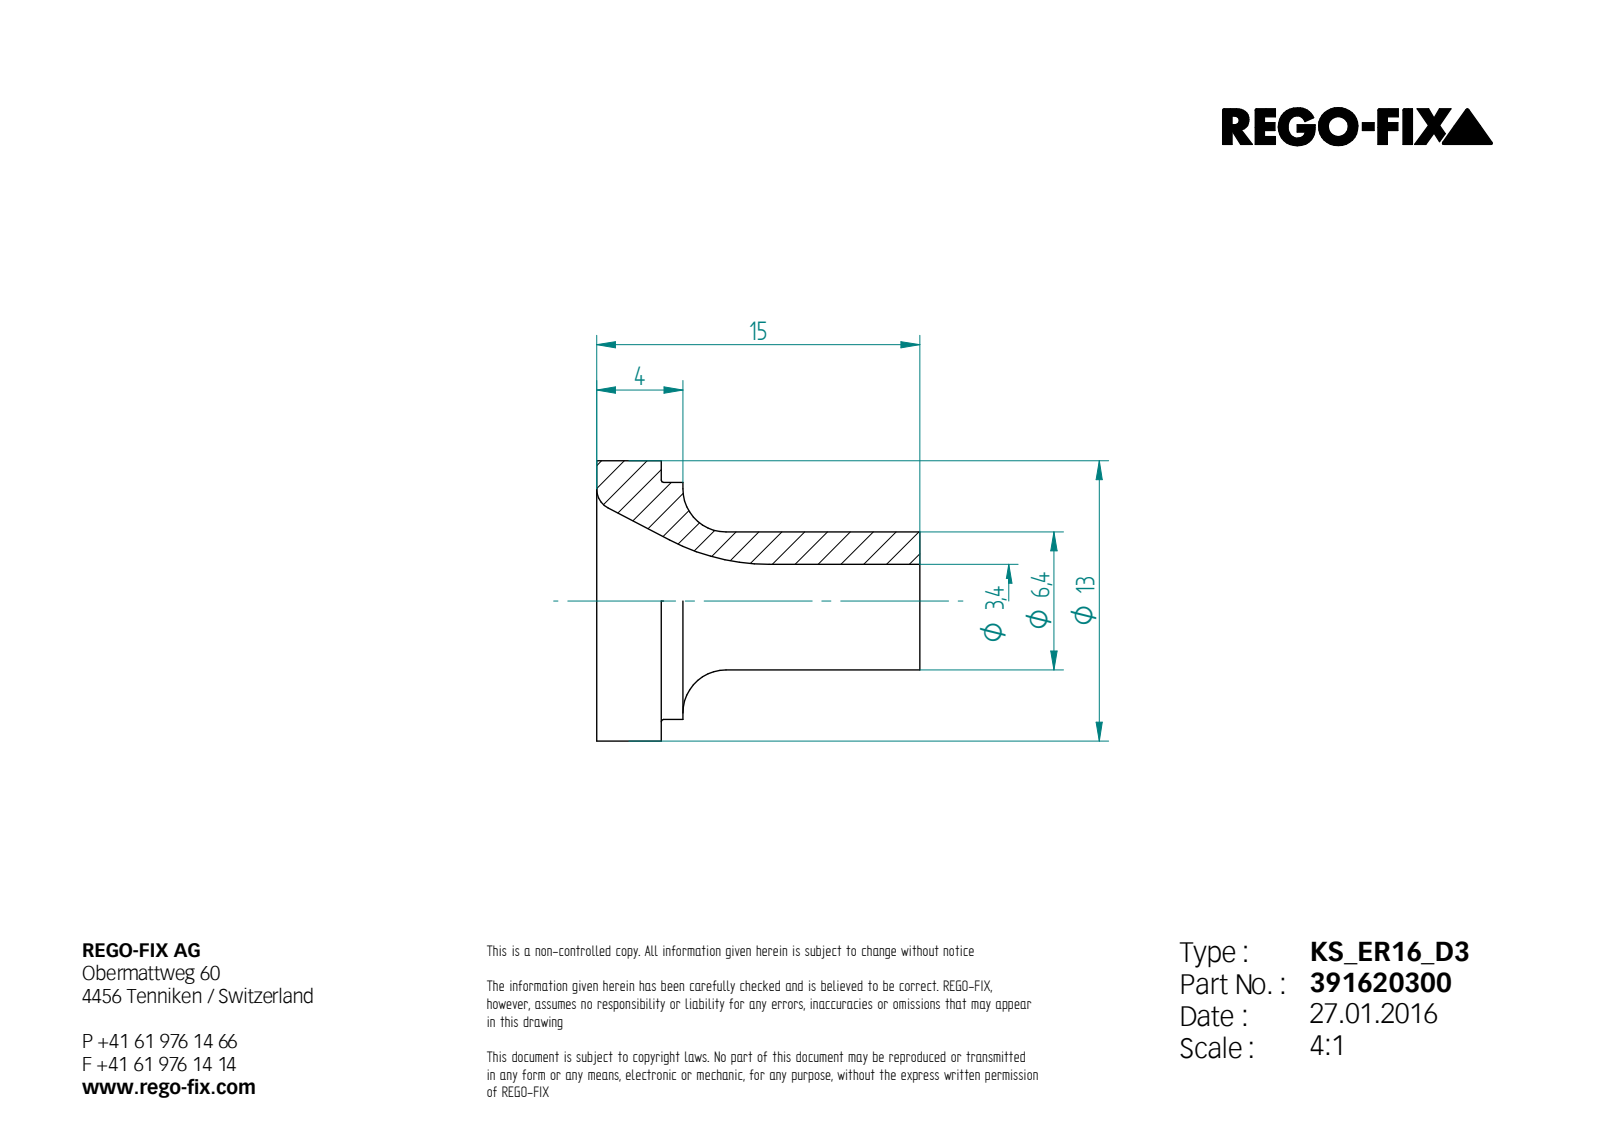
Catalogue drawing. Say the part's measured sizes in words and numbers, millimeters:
Its 3-D file was written by "Unknown (AUTOMOTIVE_DESIGN)". It is 1 solid with 13 faces: 4 planar, 4 cylindrical and 5 other. Overall it measures 15 by 13 by 13 millimeters. Its volume is 589 cubic millimeters and its surface area 774 square millimeters. Round holes: 1 of diameter 3.4. Round bosses or shafts: 1 of diameter 13, 1 of diameter 11, 1 of diameter 6.4. The main face-to-face distances are 3, 15, 12, 4, 1, 11.
